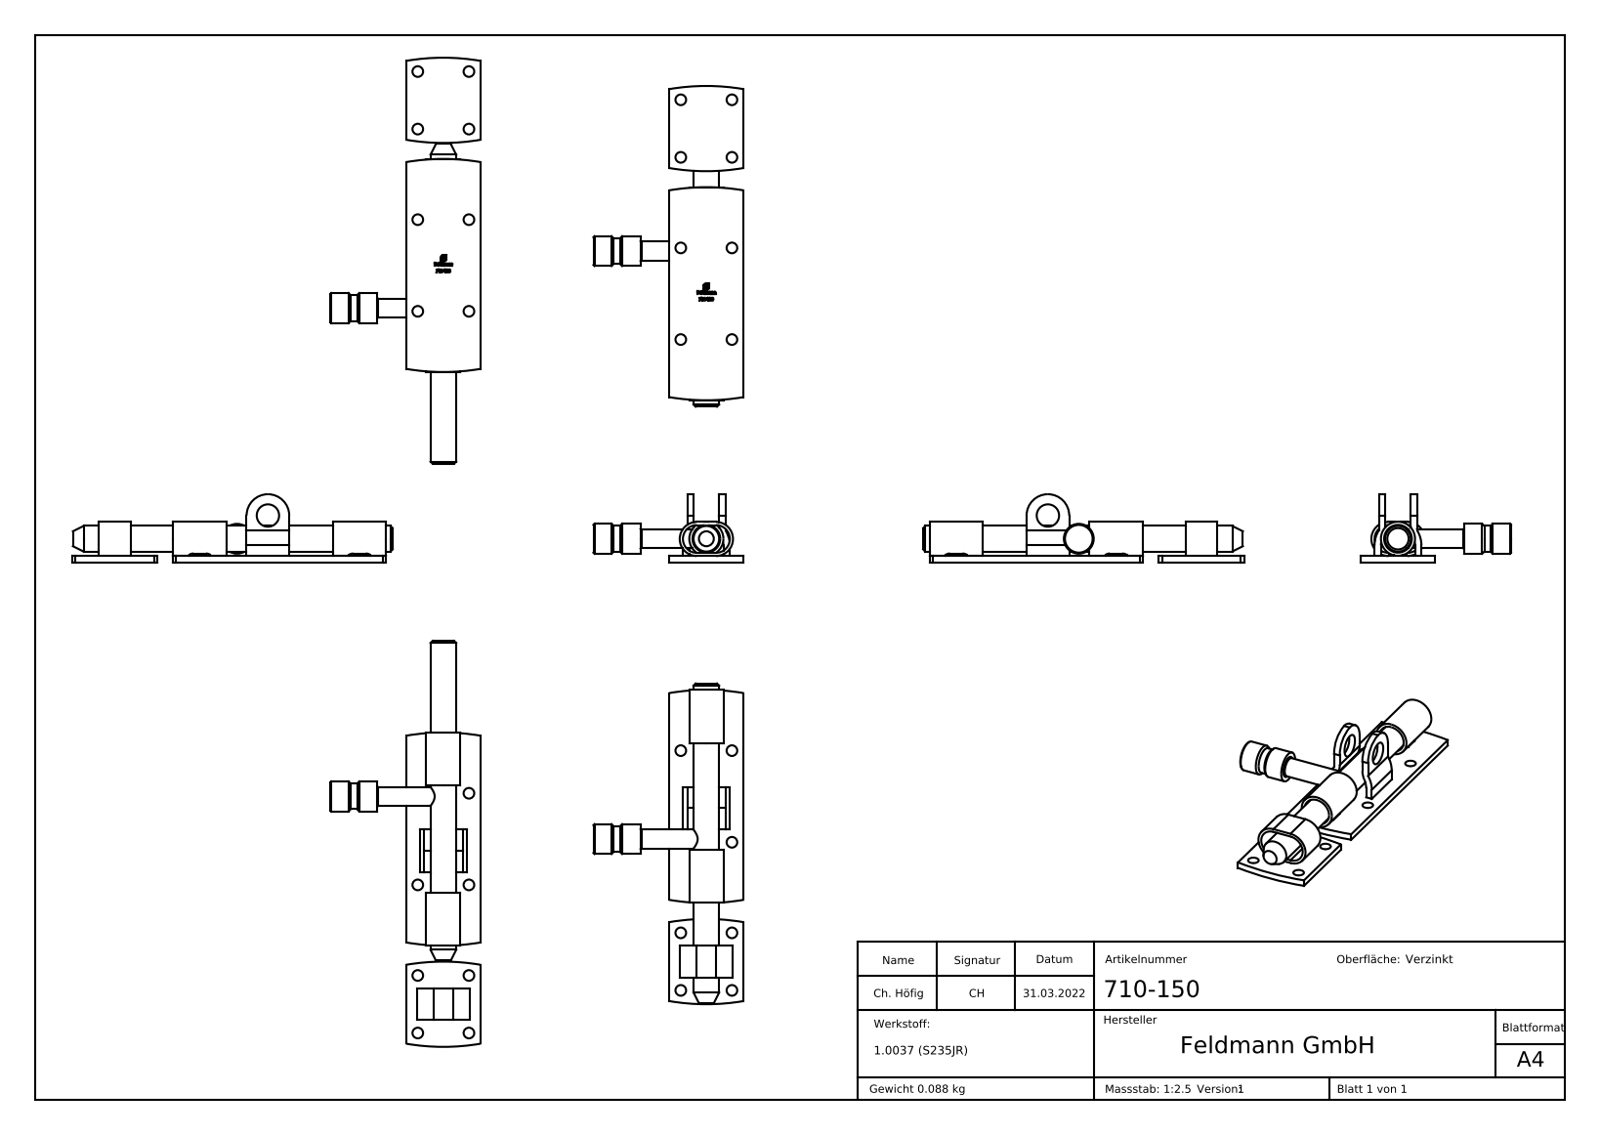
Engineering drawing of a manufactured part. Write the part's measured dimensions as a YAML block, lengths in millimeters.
part_name: "710-XX0 Teil1_710-150 Teil1; 710-XX0 Teil2_710-150 Teil2; 710-150; 710-XX0 Teil3_710-150 Teil3"
step_written_by: "SolidWorks 2018 (CONFIG_CONTROL_DESIGN)"
units: millimeters
bodies: {solids: 3, faces: 311, planar: 166, cylindrical: 45, other: 100}
overall_size: [150.5, 70.5, 32]
volume: 43169
surface_area: 27297
round_holes:
  - {diameter: 5, count: 8}
  - {diameter: 10.5, count: 1}
  - {diameter: 13, count: 1}
round_bosses_or_shafts:
  - {diameter: 12, count: 2}
  - {diameter: 16, count: 1}
  - {diameter: 14, count: 1}
  - {diameter: 8.8, count: 1}
partial_cylinders:
  - {radius: 2, count: 8}
  - {radius: 102.83, count: 4}
  - {radius: 10, count: 3}
  - {radius: 6.5, count: 2}
  - {radius: 8, count: 2}
  - {radius: 10.25, count: 2}
  - {radius: 13.25, count: 2}
face_to_face_distances: [3, 35, 15, 20, 2, 8.5, 26.5, 17, 11.5, 23.5]
hole_center_spacings: [24, 27, 36.12, 42.5, 43, 48.81, 49.24, 69.5]
